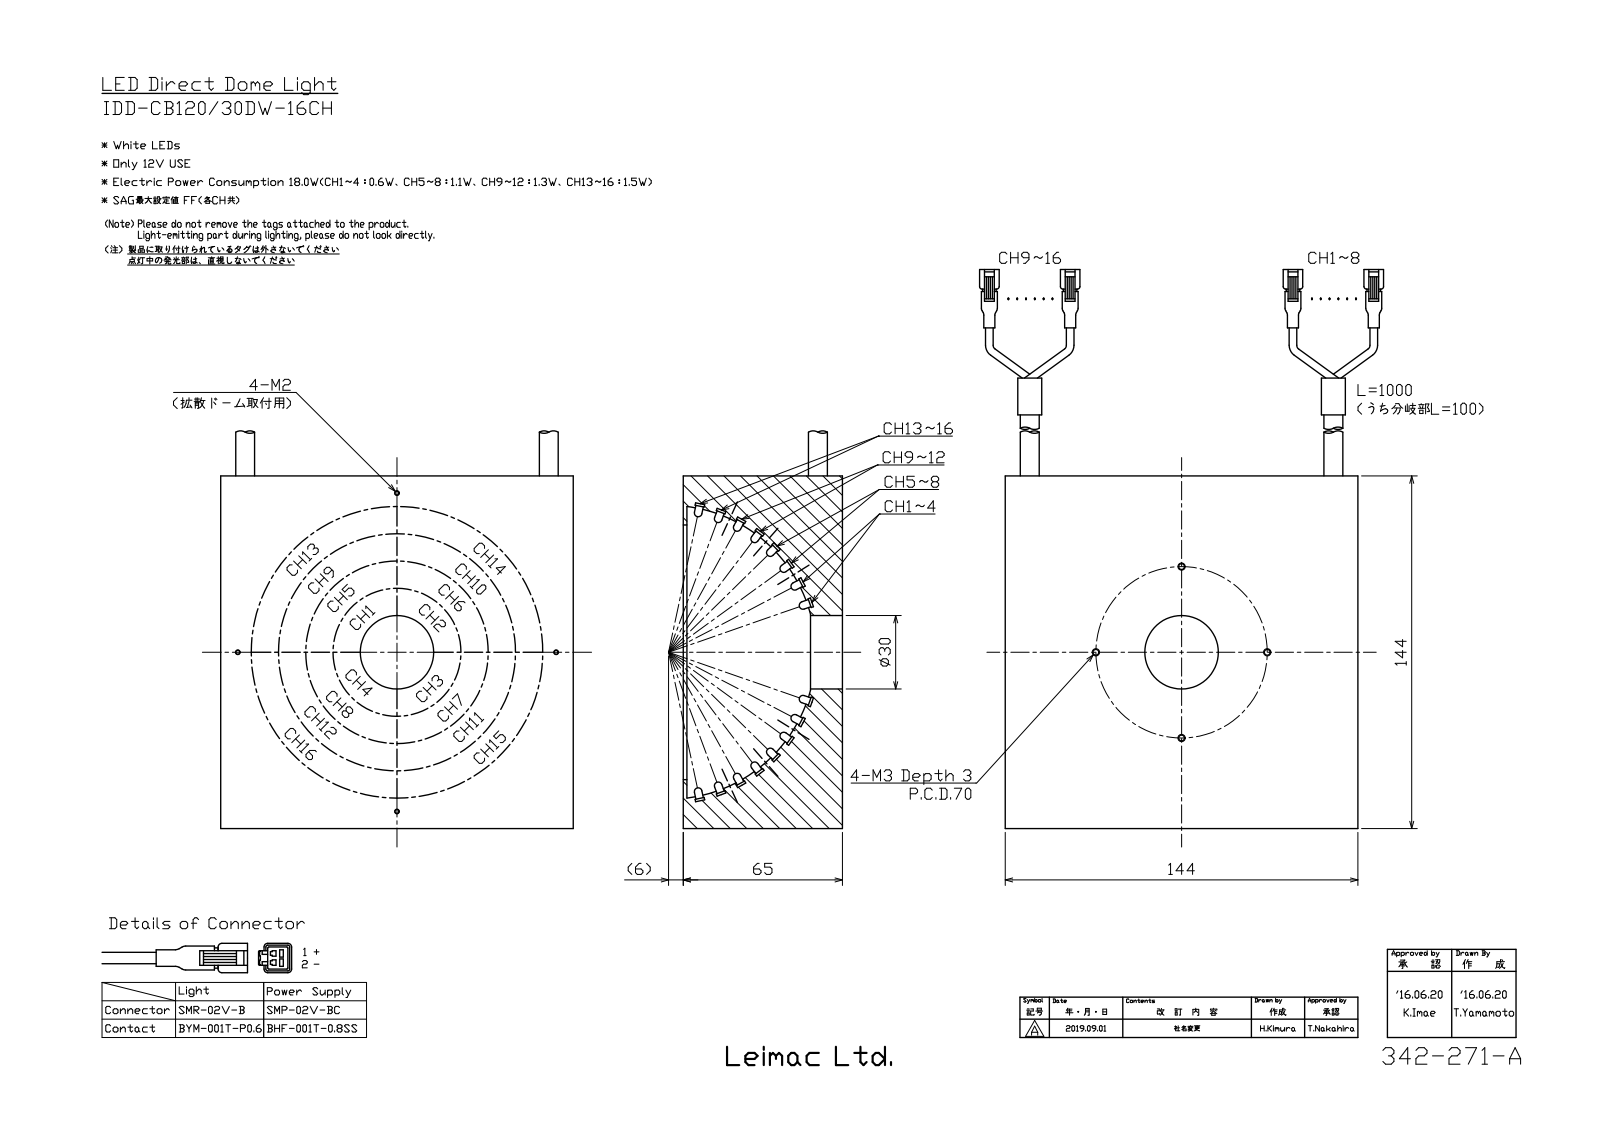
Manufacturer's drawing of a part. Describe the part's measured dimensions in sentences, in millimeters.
Its 3-D file was written by "SolidWorks 2014 (CONFIG_CONTROL_DESIGN)". It is 1 solid with 82 faces: 23 planar, 38 cylindrical and 21 other. Overall it measures 234.59 by 147.7 by 65 millimeters. Its volume is 1 044 000 cubic millimeters and its surface area 93 756 square millimeters. Round holes: 4 of diameter 1.6, 4 of diameter 2.5, 1 of diameter 30, 1 of diameter 113. Round bosses or shafts: 12 of diameter 3.7, 2 of diameter 8, 2 of diameter 7.7. Partial cylindrical surfaces (rounded edges, fillets, slot ends): 12 of radius 1.5. The main face-to-face distances are 144, 65, 1.5, 63.5, 58.5, 202.5, 32.09, 90.59, 234.59, 53.9. The hole center spacings are 73.82, 30, 35, 49.5, 65, 91.92, 100, 70.
